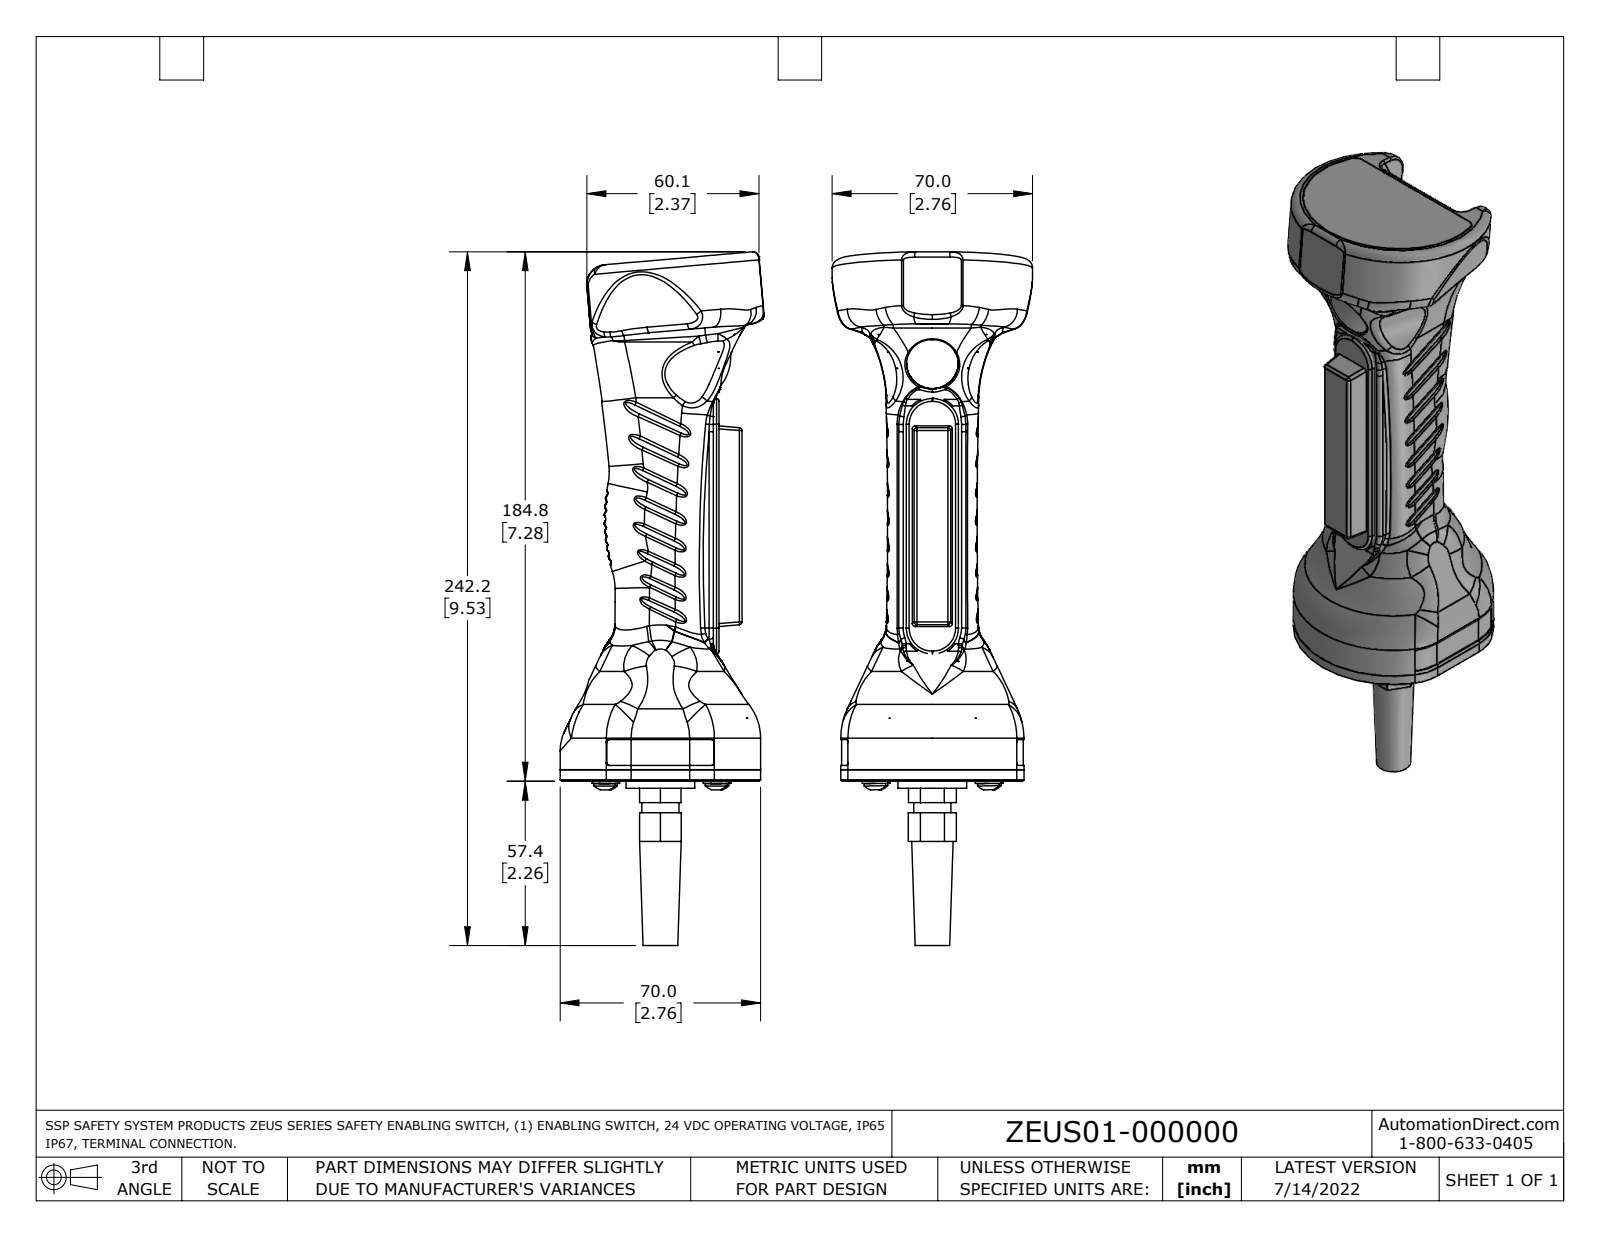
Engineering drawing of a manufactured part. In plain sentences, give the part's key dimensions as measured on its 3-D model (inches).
The part is named "ZEUS01-000000". Its 3-D file was written by "SolidWorks 2021 (AUTOMOTIVE_DESIGN)". It is 16 solids with 1127 faces: 318 planar, 394 cylindrical and 415 other. Overall it measures 9.535 by 2.803 by 2.756 inches. Its volume is 23.26 cubic inches and its surface area 117.8 square inches. Round holes: 4 of diameter 0.132, 4 of diameter 0.169, 4 of diameter 0.177, 4 of diameter 0.197, 2 of diameter 0.098, 2 of diameter 0.11, 2 of diameter 0.165, 2 of diameter 0.331, 1 of diameter 0.551, 1 of diameter 0.709, 1 of diameter 0.728, 1 of diameter 0.787. Round bosses or shafts: 4 of diameter 0.354, 4 of diameter 0.295, 4 of diameter 0.157, 4 of diameter 0.039, 2 of diameter 0.236, 1 of diameter 0.945, 1 of diameter 0.827, 1 of diameter 0.776. Partial cylindrical surfaces (rounded edges, fillets, slot ends): 96 of radius 0.005, 51 of radius 0.039, 48 of radius 0.028, 21 of radius 0.079, 10 of radius 0.118, 7 of radius 0.031, 5 of radius 0.012, 4 of radius 0.618. The main face-to-face distances are 0.157, 0.079, 0.014, 0.02, 0.065, 0.059, 0.098, 0.177, 0.571, 0.256. The hole center spacings are 1.531, 0.866, 1.181, 0.63, 1.558, 2.184, 0.404, 0.404.
